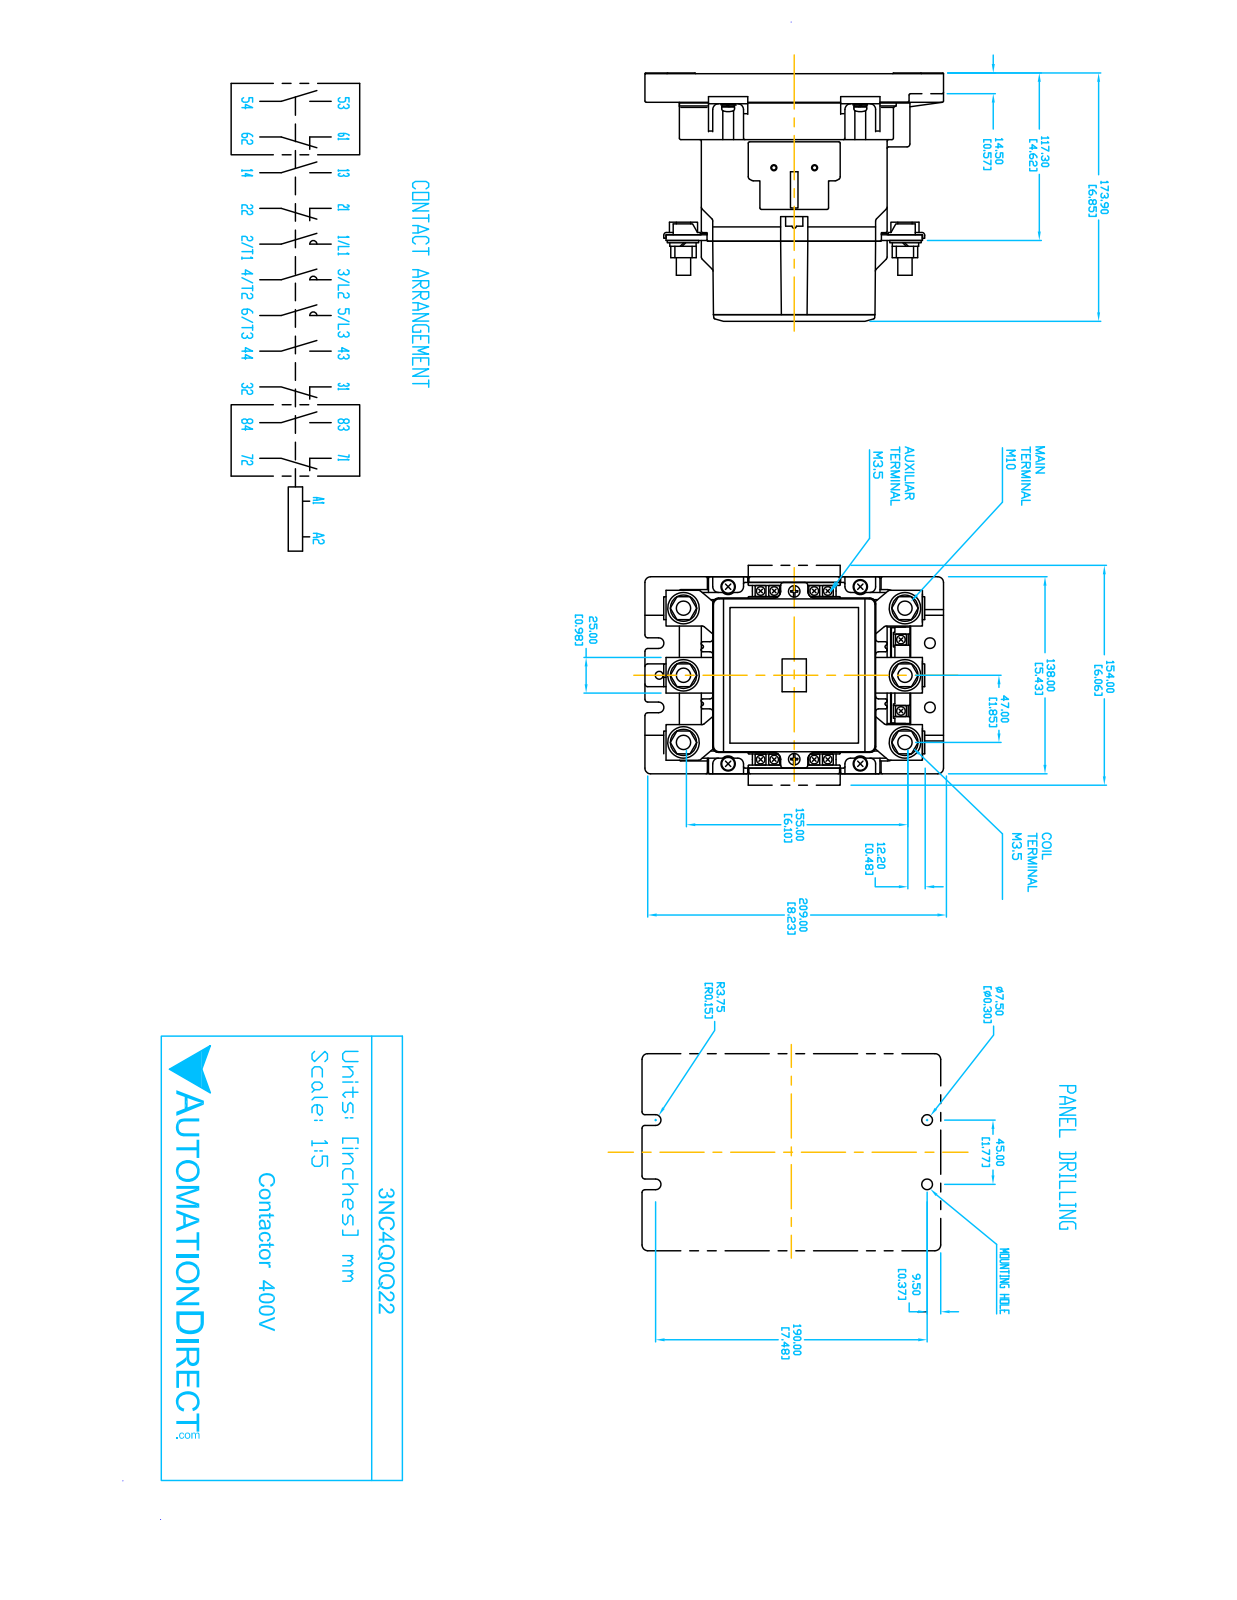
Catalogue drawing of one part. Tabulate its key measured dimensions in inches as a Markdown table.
| quantity | value |
| --- | --- |
| part name | 3NC4Q0Q22 |
| STEP written by | SolidWorks 2018 (AUTOMOTIVE_DESIGN) |
| units | inches |
| bodies | 20 solids, 376 faces (258 planar, 118 cylindrical, 0 other) |
| overall size | 8.228 × 6.929 × 5.433 |
| volume | 179.6 in³ |
| surface area | 327 in² |
| round holes (diameter × count) | 0.315 × 8, 0.394 × 6, 0.295 × 2 |
| partial cylindrical surfaces (radius × count) | 0.079 × 22, 0.157 × 16, 0.031 × 8, 0.039 × 8, 0.197 × 4, 0.217 × 4, 0.02 × 2, 0.148 × 2 |
| main face-to-face distances | 4.72, 4.843, 0.591, 4.736, 0.016, 4.252, 6.929, 2.209, 2.193, 0.315 |
| hole center spacings | 1.85, 3.087, 3.835, 5.17, 6.377, 6.102, 1.122, 1.185 |
